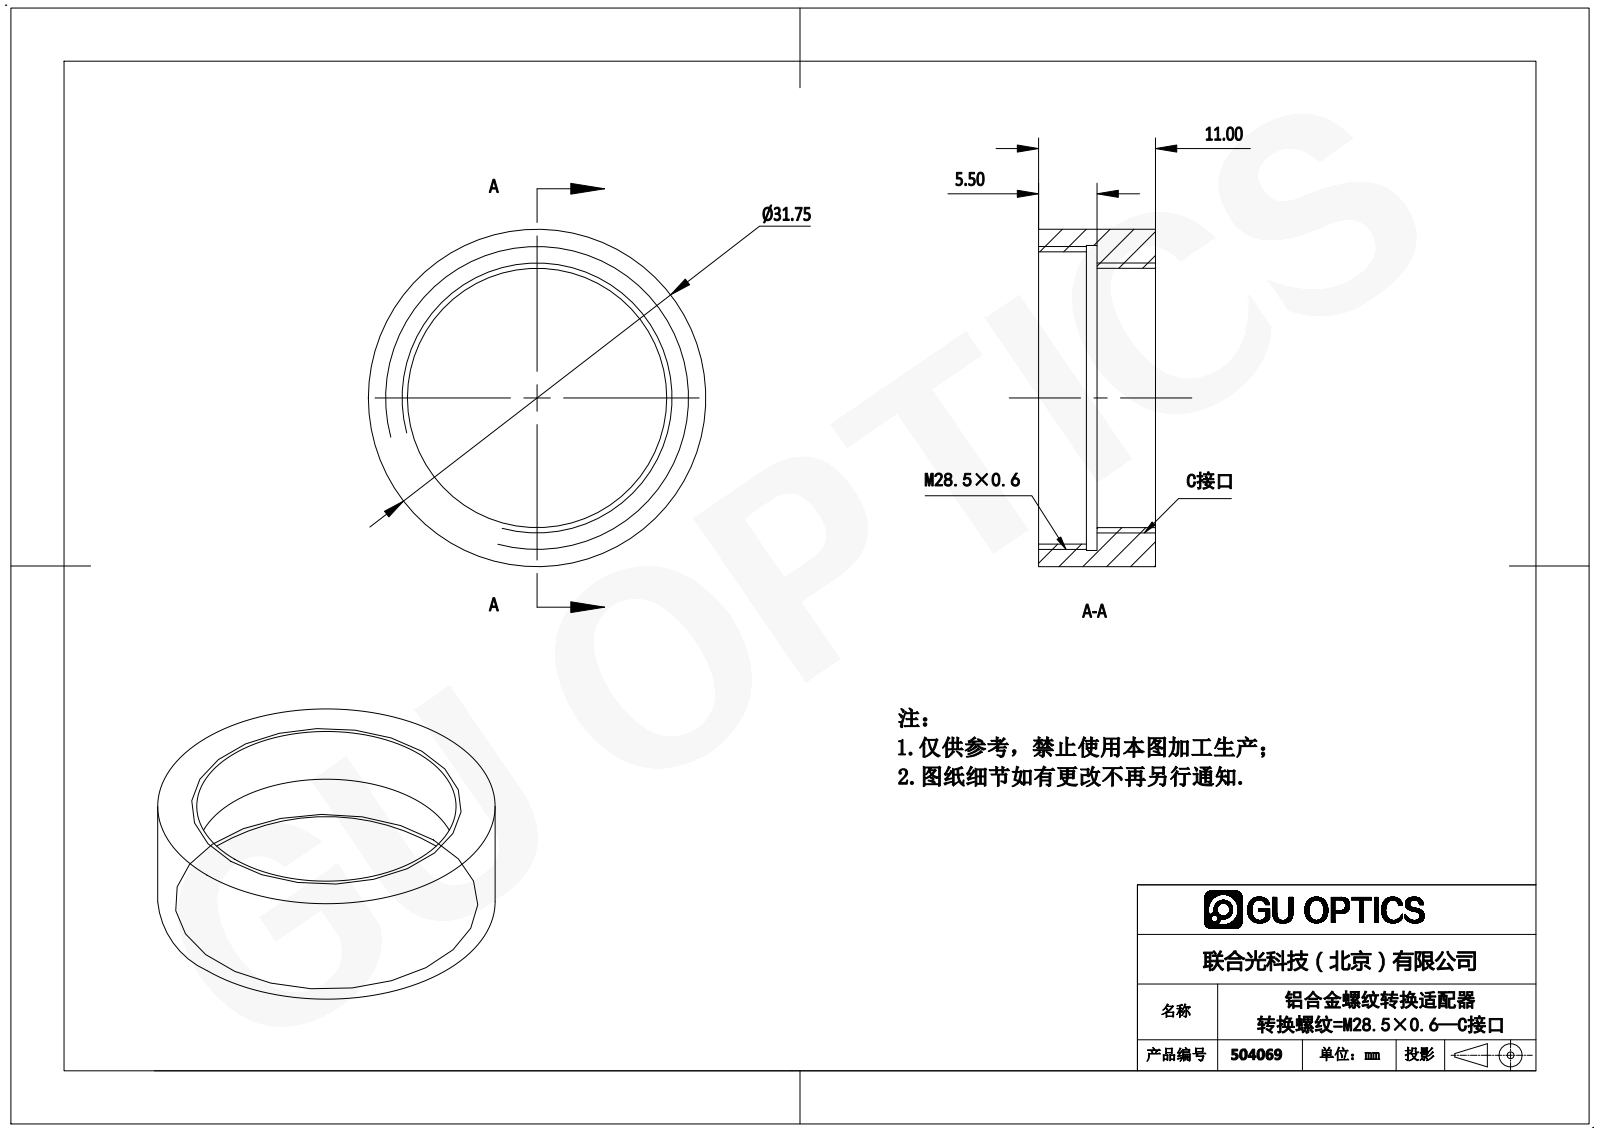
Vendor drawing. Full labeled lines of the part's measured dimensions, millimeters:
Part name (STEP PRODUCT): 504069
STEP written by: SolidWorks 2016 (AUTOMOTIVE_DESIGN)
Units: millimetres
Bodies: 1 solid, 12 faces (4 planar, 8 cylindrical, 0 other)
Overall size (bounding box): 31.75 × 31.75 × 11
Volume: 2 818 mm³ · Surface area: 2 752 mm²
Round holes (diameter × count): ⌀24.4 ×1, ⌀27.5 ×1, ⌀28.7 ×1
Round bosses / shafts (diameter × count): ⌀31.75 ×1
Main face-to-face distances: 5.5, 11, 4.5, 1, 6.5
